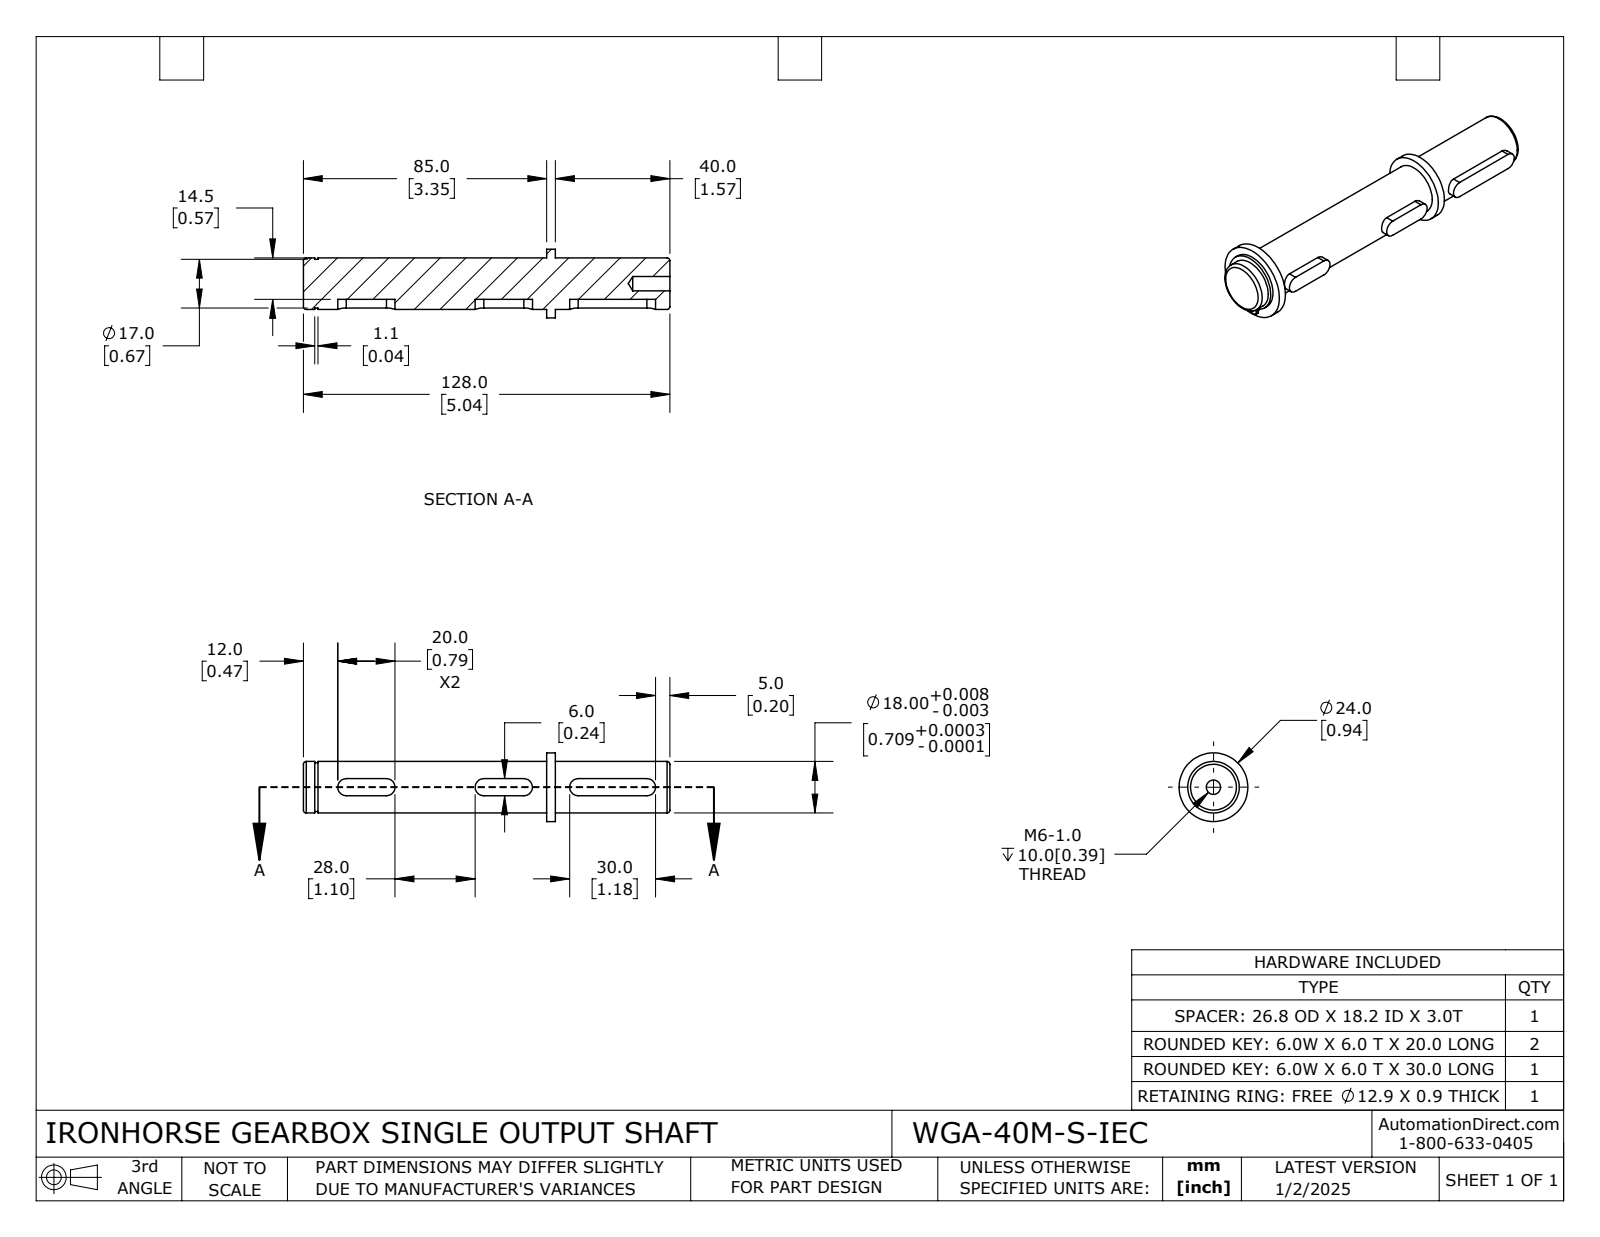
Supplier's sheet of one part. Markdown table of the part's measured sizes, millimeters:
| quantity | value |
| --- | --- |
| part name | WGA-40M-S-IEC |
| STEP written by | SolidWorks 2024 (CONFIG_CONTROL_DESIGN) |
| units | millimeters |
| bodies | 6 solids, 91 faces (37 planar, 48 cylindrical, 6 other) |
| overall size | 128 × 26.8 × 26.8 |
| volume | 34 938 mm³ |
| surface area | 12 059 mm² |
| round holes (diameter × count) | 1.3 × 2, 5 × 1, 17 × 1, 18.2 × 1 |
| round bosses / shafts (diameter × count) | 26.8 × 1, 24 × 1, 20.45 × 1, 18 × 1 |
| partial cylindrical surfaces (radius × count) | 3 × 6, 0.5 × 2, 2.2 × 2 |
| main face-to-face distances | 6, 3, 79.9, 5.1, 8.1, 85, 76.9, 88, 82.9, 128 |
| hole center spacings | 10.48, 2.4 |
